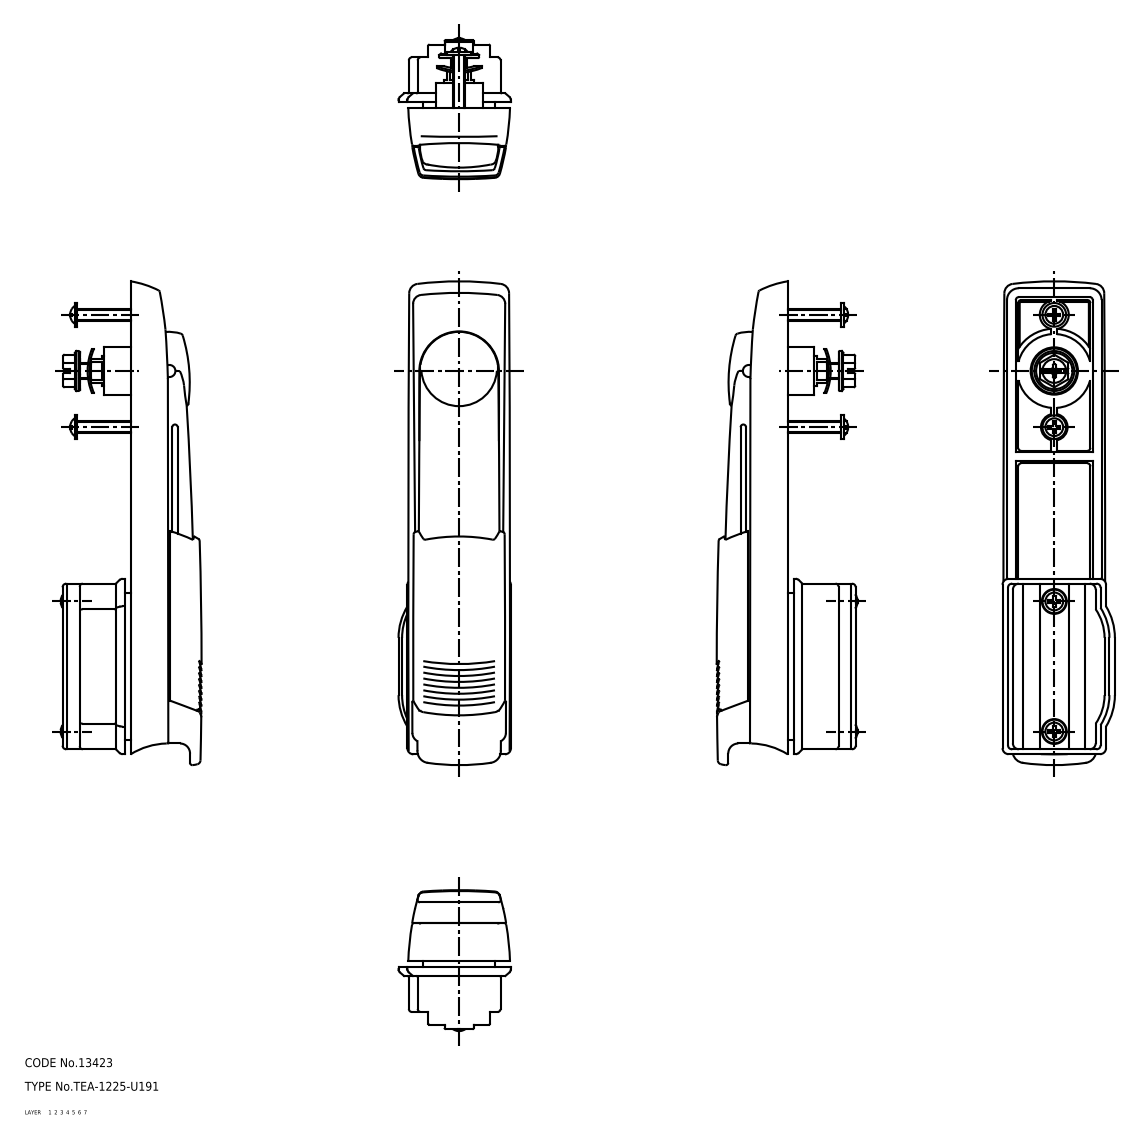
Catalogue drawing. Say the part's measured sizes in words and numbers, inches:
The part is named "handle; cover; bracket; base (+2 more)". Its 3-D file was written by "CADfix (AUTOMOTIVE_DESIGN)". It is 5 solids with 529 faces: 0 planar, 0 cylindrical and 529 other. Overall it measures 6.443 by 1.935 by 1.496 inches. Its volume is 5.631 cubic inches and its surface area 77.78 square inches.
